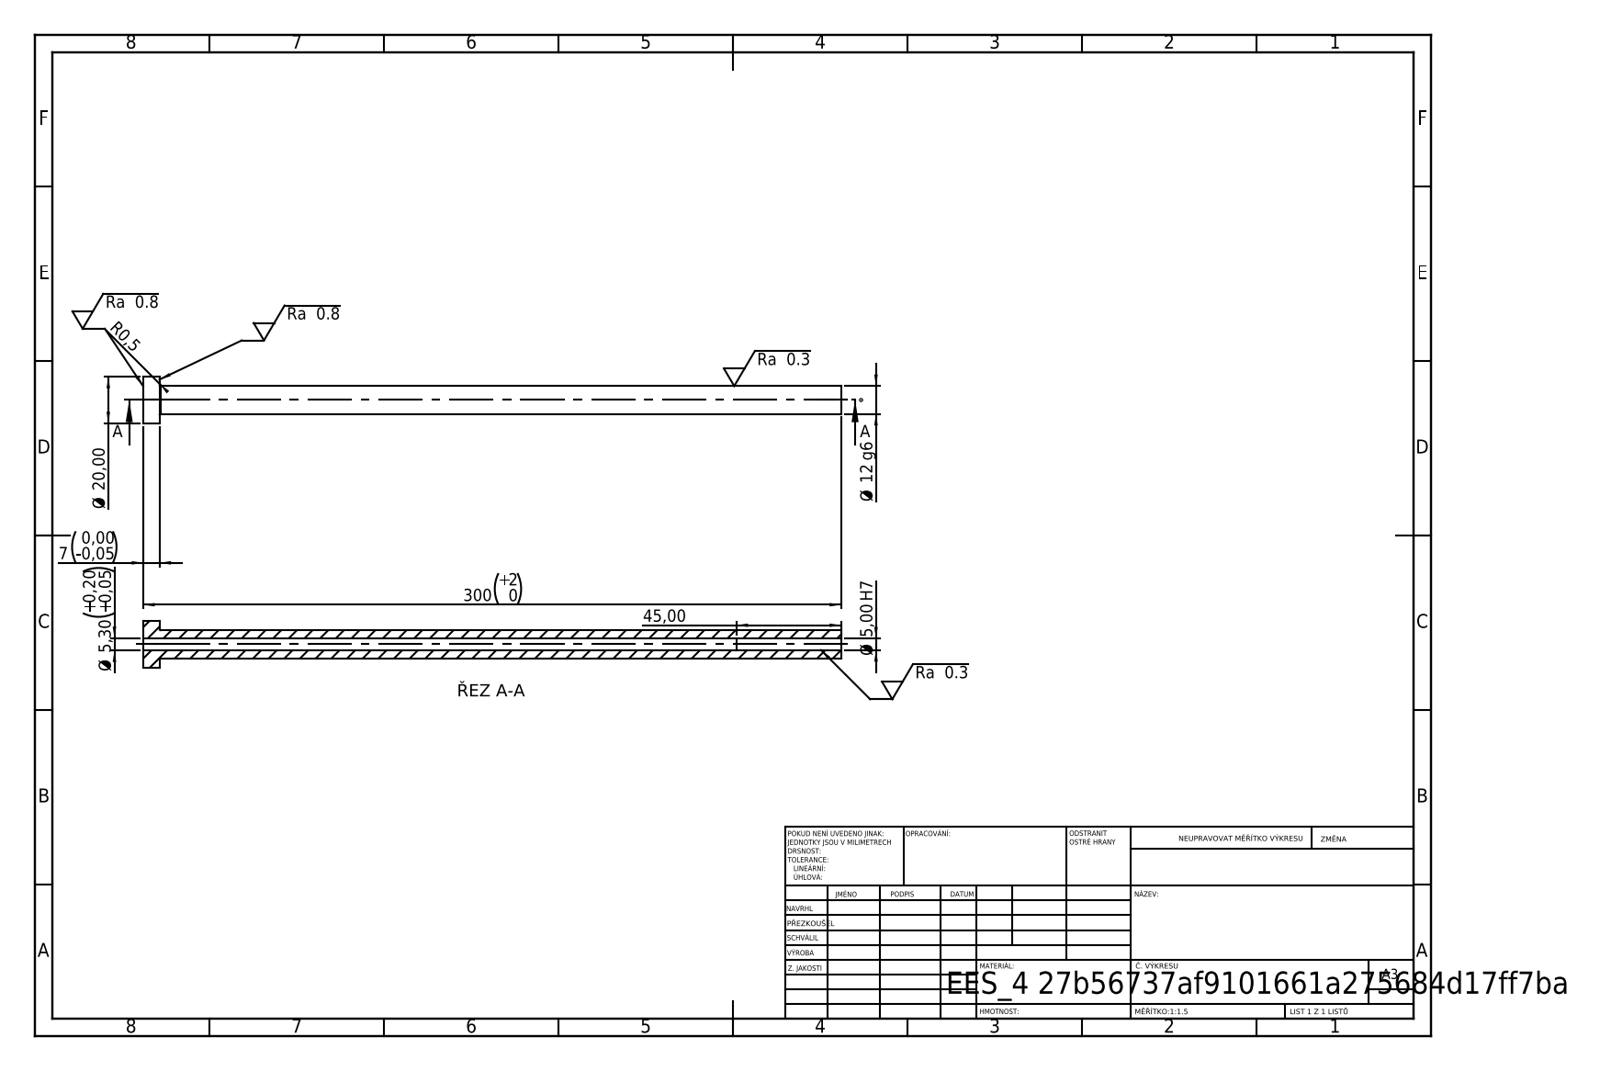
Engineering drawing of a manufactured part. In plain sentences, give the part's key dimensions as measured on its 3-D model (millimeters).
Its 3-D file was written by "SolidWorks 2019 (CONFIG_CONTROL_DESIGN)". It is 1 solid with 14 faces: 4 planar, 8 cylindrical and 2 other. Overall it measures 300 by 20 by 20 millimeters. Its volume is 28 829 cubic millimeters and its surface area 17 019 square millimeters. Round holes: 1 of diameter 5, 1 of diameter 5.3. Round bosses or shafts: 1 of diameter 20, 1 of diameter 12. The main face-to-face distances are 7, 300, 293, 255, 248, 45.
